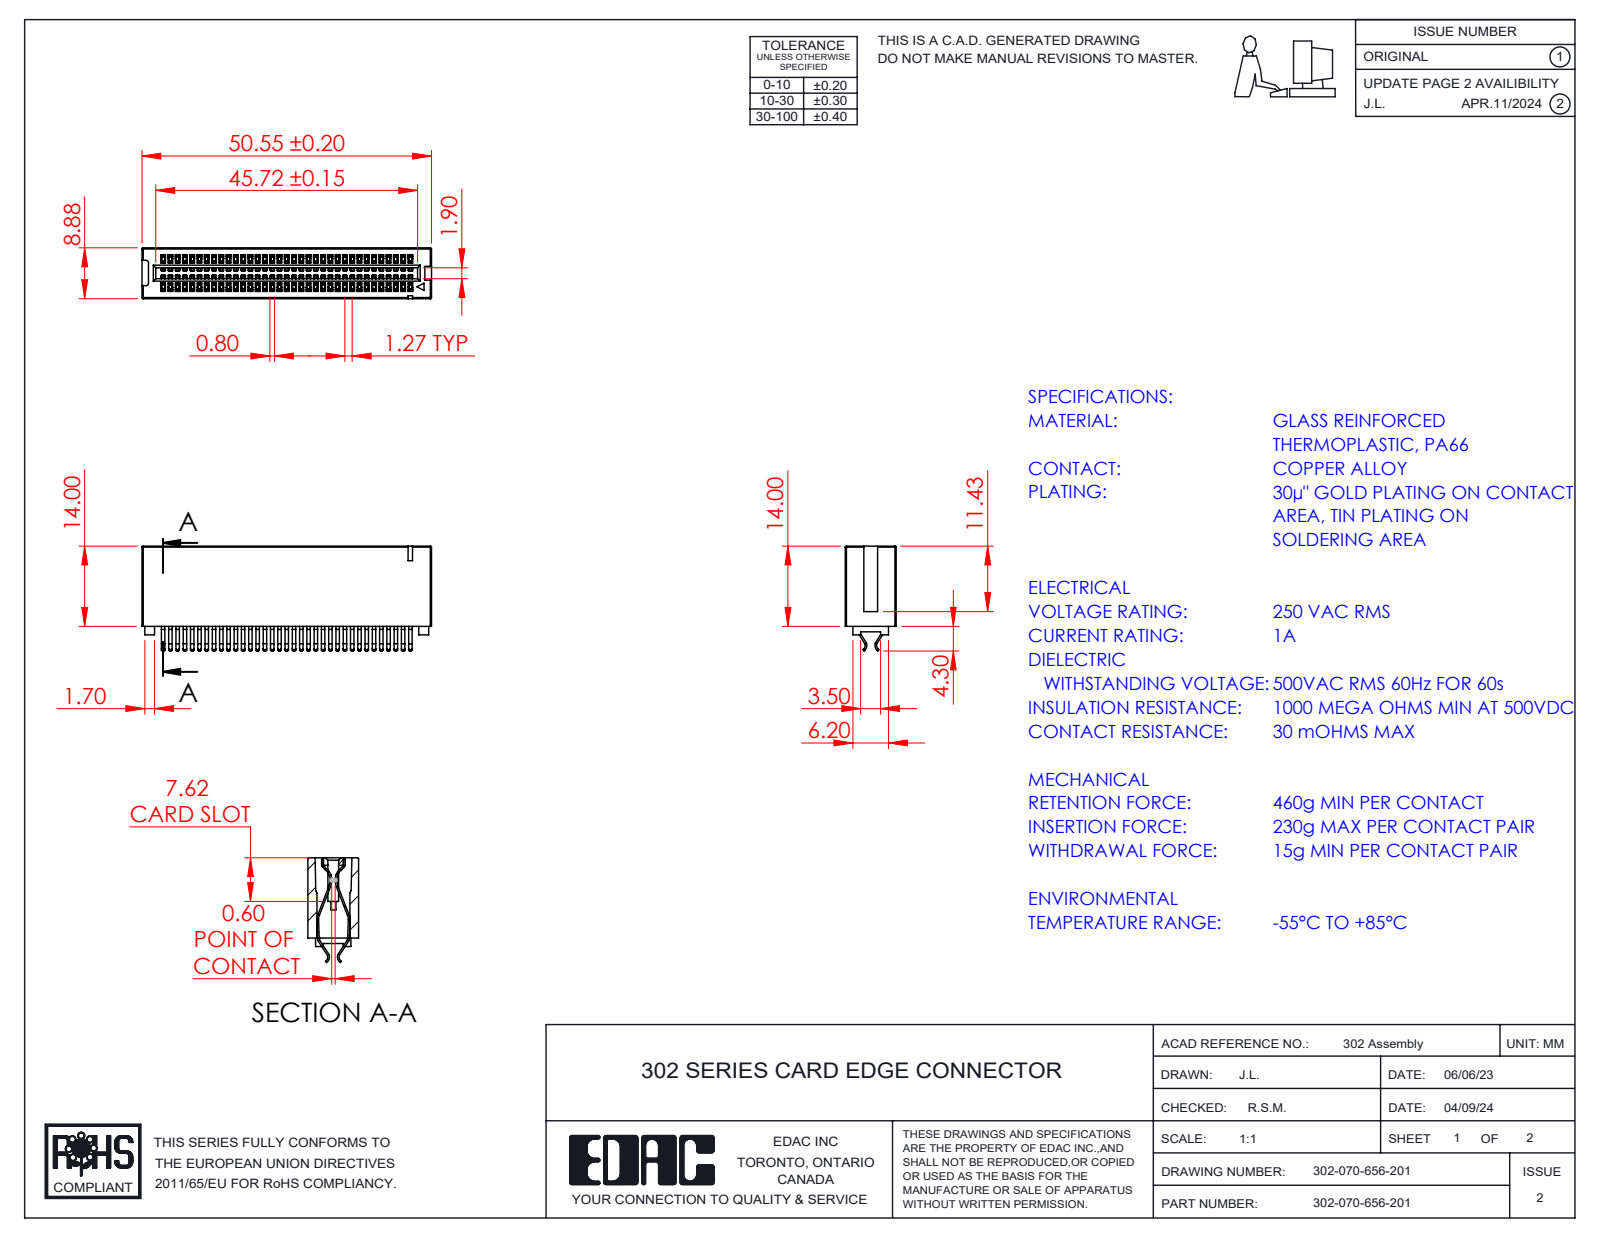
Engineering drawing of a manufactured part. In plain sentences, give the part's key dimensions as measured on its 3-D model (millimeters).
The part is named "302-070-656-201; Contact_302-290-X56; HSG_Vertical HSG". Its 3-D file was written by "SolidWorks 2023 (CONFIG_CONTROL_DESIGN)". It is 71 solids with 3391 faces: 2254 planar, 1133 cylindrical and 4 other. Overall it measures 50.55 by 18.3 by 8.88 millimeters. Its volume is 3 941 cubic millimeters and its surface area 10 855 square millimeters. Partial cylindrical surfaces (rounded edges, fillets, slot ends): 218 of radius 0.2, 2 of radius 0.11, 2 of radius 0.4, 2 of radius 0.41, 2 of radius 0.93, 2 of radius 1.05, 2 of radius 1.23, 2 of radius 1.25. The main face-to-face distances are 1.27, 2.54, 3.81, 5.08, 6.35, 7.62, 8.88, 8.89, 10.16, 11.43.
